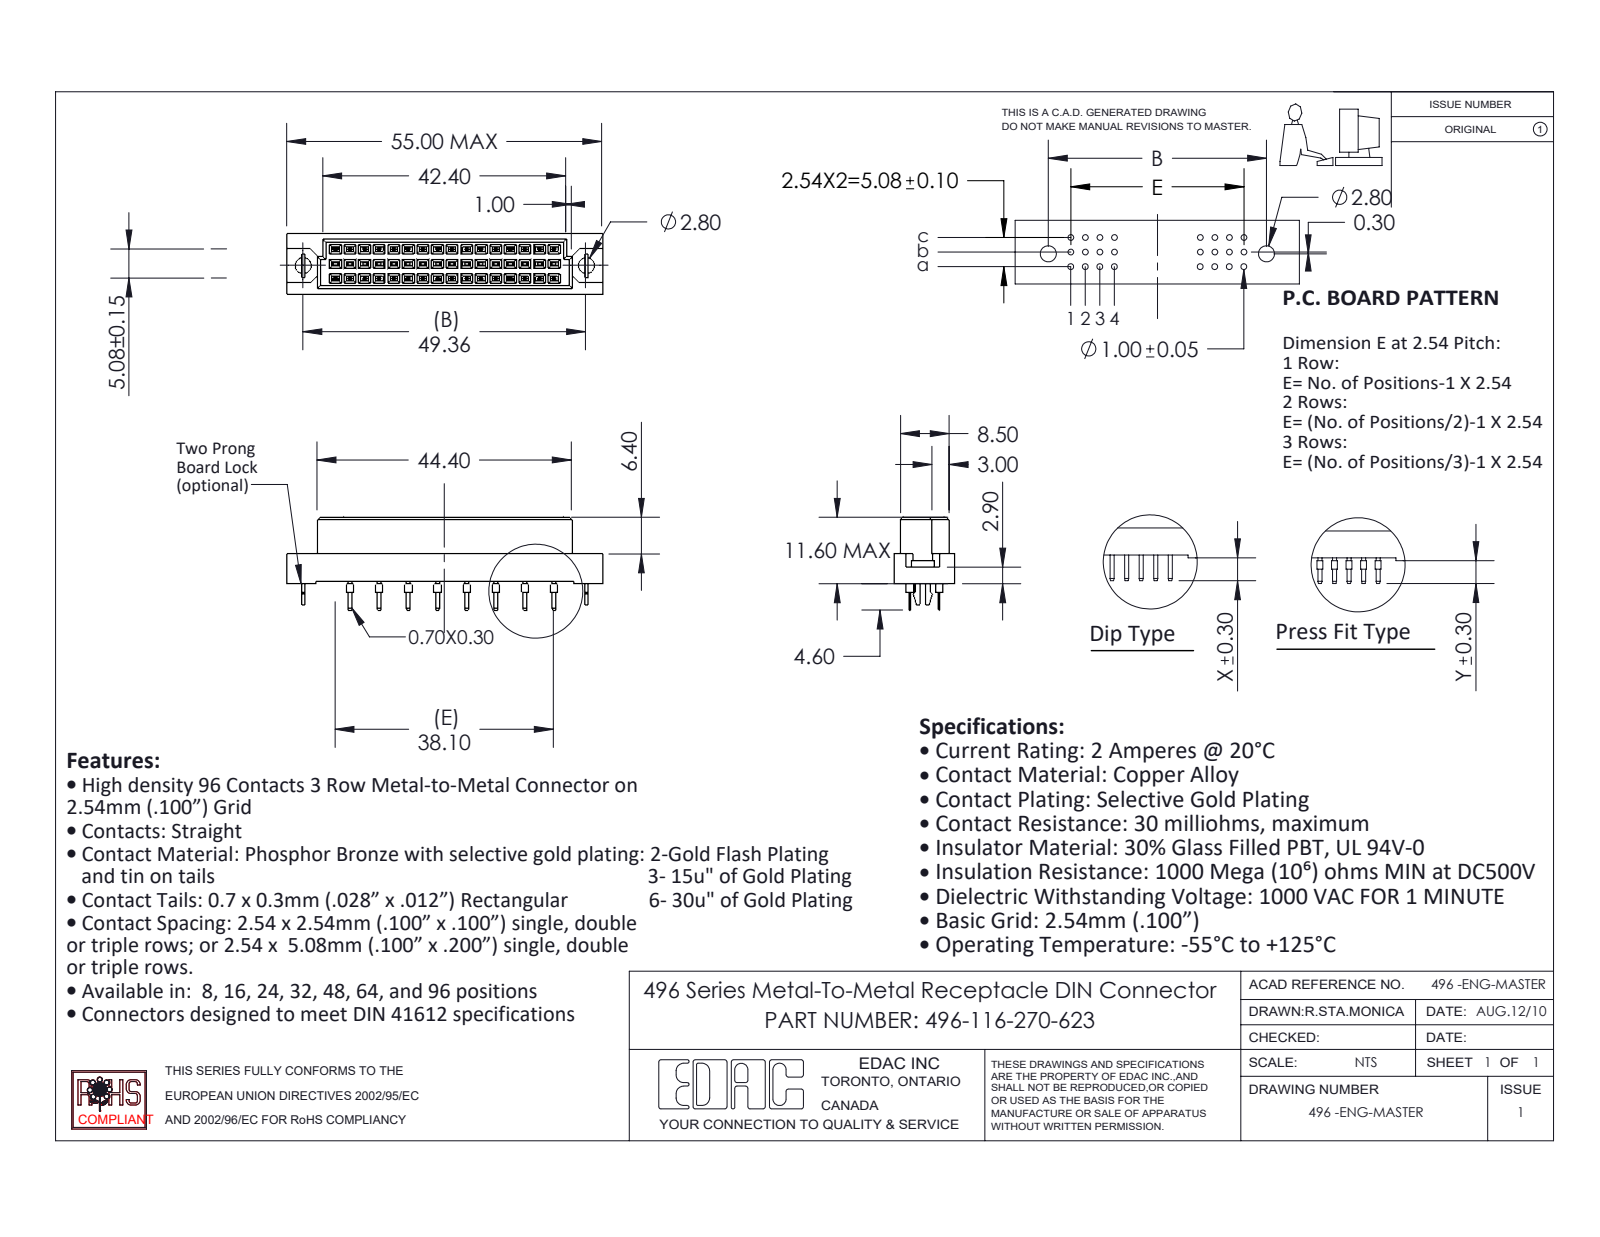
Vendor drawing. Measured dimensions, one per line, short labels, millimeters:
name: 496-290_70; 496-116-270-623; 496 Part_48; 496 Bore-lock
written by: SolidWorks 2020 (CONFIG_CONTROL_DESIGN)
unit: mm
bodies: 19 solids, 990 faces (952 planar, 38 cylindrical, 0 other)
size: 55 × 16.2 × 10.6
volume: 4 656 mm³; area: 4 666 mm²
holes: 2× ⌀2.8
bosses: 16× ⌀1
rounds: 1× R0.53
face distances: 2.54, 5.08, 1.05, 9.55, 0.81, 10.6, 0.56, 3.35, 1.73, 8.5
hole spacings: 49.36
